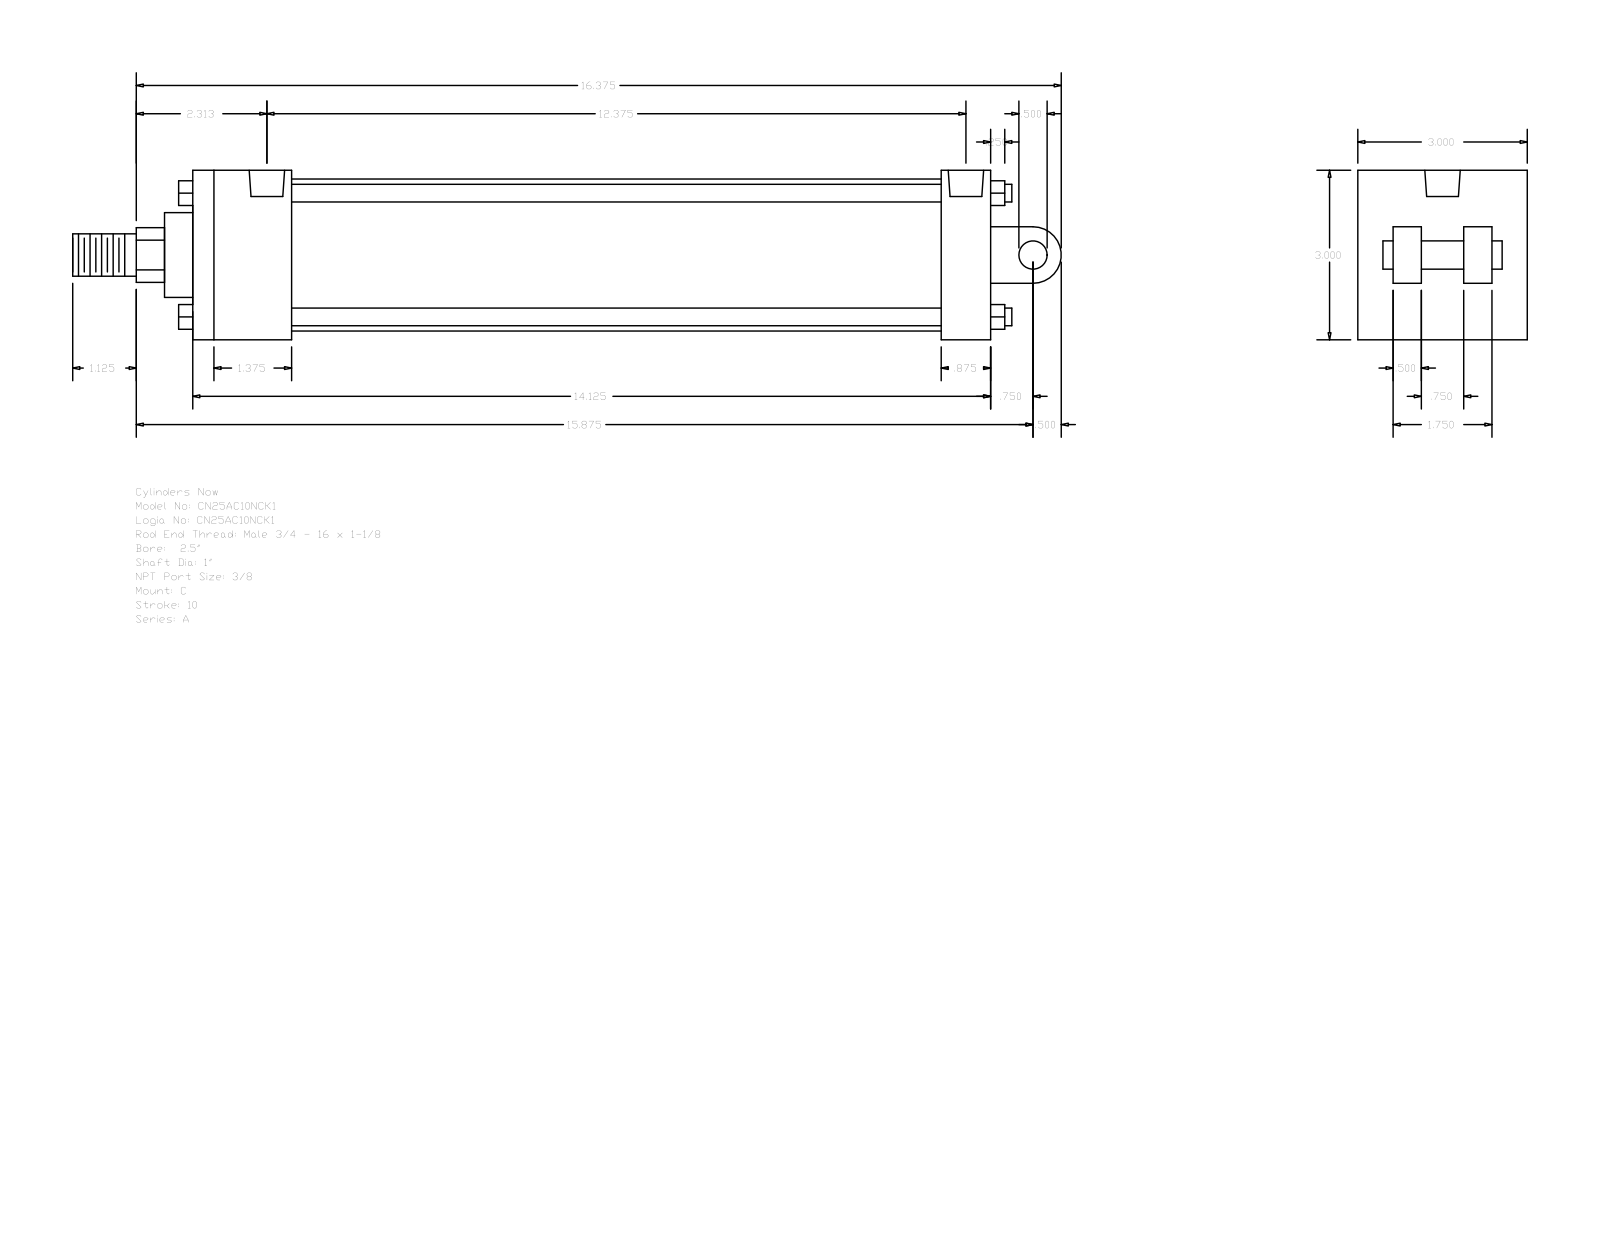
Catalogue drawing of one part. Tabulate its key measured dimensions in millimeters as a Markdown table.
| quantity | value |
| --- | --- |
| part name | A_C__0250_1 |
| STEP written by | GSSL Pune (CONFIG_CONTROL_DESIGN) |
| units | millimeters |
| bodies | 0 solids, 135 faces (102 planar, 33 cylindrical, 0 other) |
| overall size | 444.5 × 76.2 × 76.2 |
| round holes (diameter × count) | 5.56 × 4, 15.93 × 2 |
| round bosses / shafts (diameter × count) | 7.94 × 4, 68.33 × 1, 38.1 × 1, 25.4 × 1, 19.05 × 1, 12.7 × 1 |
| partial cylindrical surfaces (radius × count) | 12.29 × 1, 12.7 × 1 |
| main face-to-face distances | 76.2, 358.78, 12.7, 44.45, 336.55, 292.1, 314.33, 22.23, 15.87, 25.4 |
| hole center spacings | 2.38, 316.7, 319.08, 314.32 |
